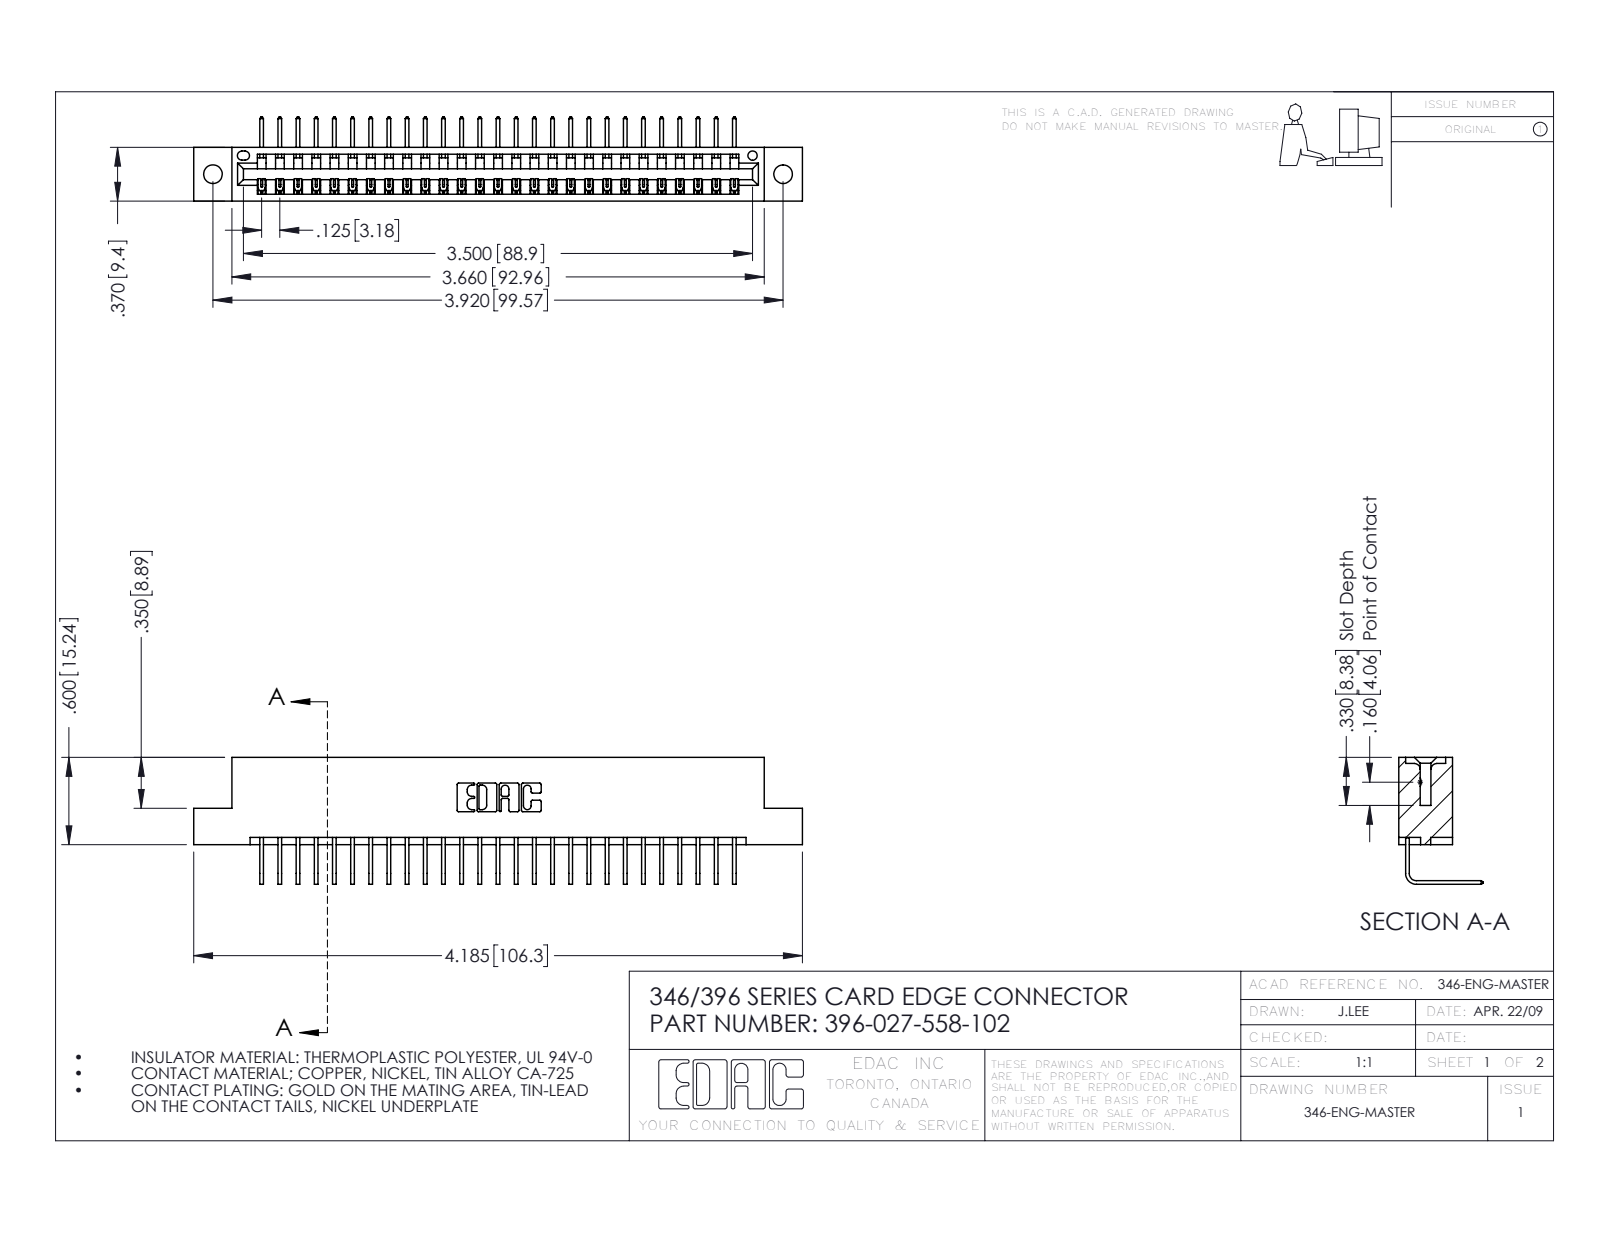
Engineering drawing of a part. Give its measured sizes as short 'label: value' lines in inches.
name: 346 Part_Flush Mounting Lugs - 0.128 Dia; 396-027-558-102; 345-292-001_558 Tail - 2
written by: SolidWorks 2016 (CONFIG_CONTROL_DESIGN)
unit: in
bodies: 28 solids, 1742 faces (1210 planar, 532 cylindrical, 0 other)
size: 4.185 × 0.873 × 0.58
volume: 0.618 in³; area: 19.78 in²
holes: 2× ⌀0.128, 1× ⌀0.064
rounds: 54× R0.006, 22× R0.01, 6× R0.007, 6× R0.031, 3× R0.026, 2× R0.031, 2× R0.04, 1× R0.014
face distances: 0.322, 0.048, 0.37, 0.25, 0.298, 0.025, 0.072, 0.148, 0.222, 0.1
hole spacings: 0.246, 3.712, 3.92
